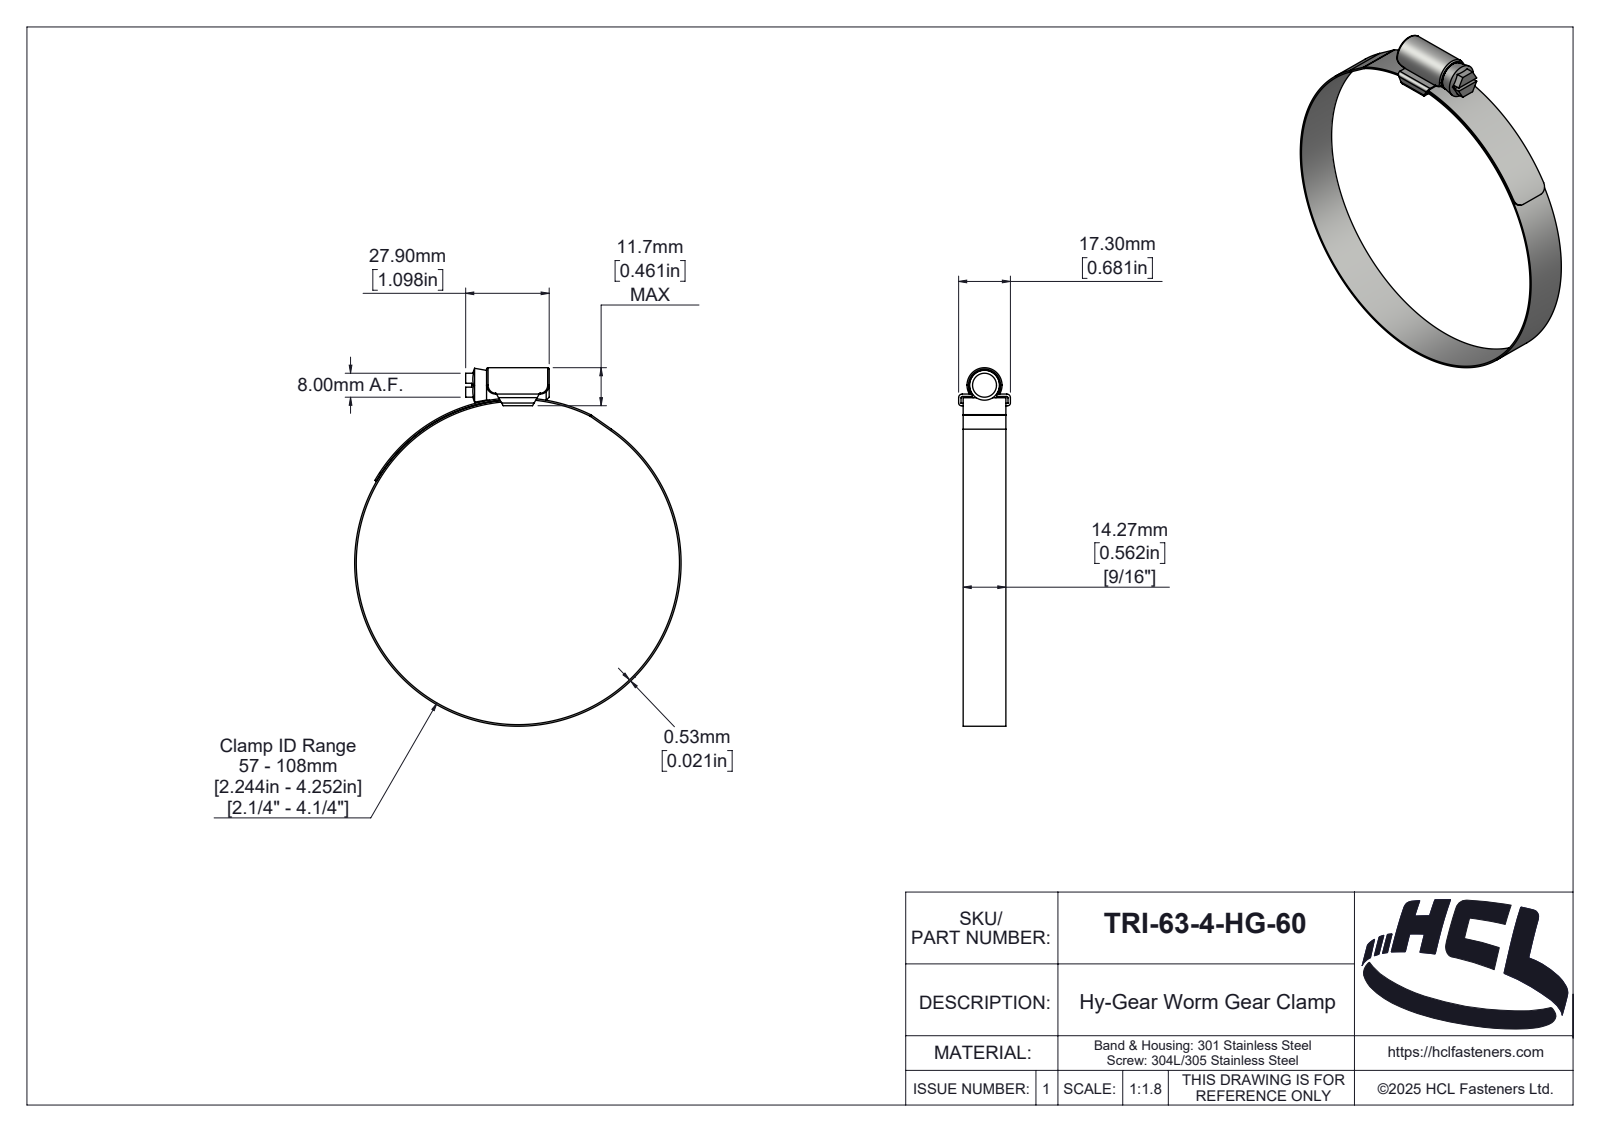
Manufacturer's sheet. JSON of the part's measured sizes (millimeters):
{"part_name": "TRI-50-0-HG-60", "step_written_by": "SolidWorks 2025 (AUTOMOTIVE_DESIGN)", "units": "millimeters", "bodies": {"solids": 3, "faces": 189, "planar": 39, "cylindrical": 89, "other": 61}, "overall_size": [119.73, 109.06, 17.3], "volume_mm3": 5806, "surface_area_mm2": 14603, "round_holes": [[108, 1]], "round_bosses_or_shafts": [[109.06, 1], [10, 1]], "partial_cylinders_radius": [[0.5, 6], [3, 4], [0.1, 2], [0.9, 2], [1.2, 2], [0.46, 1], [1.89, 1], [2, 1]], "face_to_face_distances": [0.8, 14.26, 3.1, 0.53, 2.3, 3.9, 27.9, 1.52, 15.78, 16.5]}
